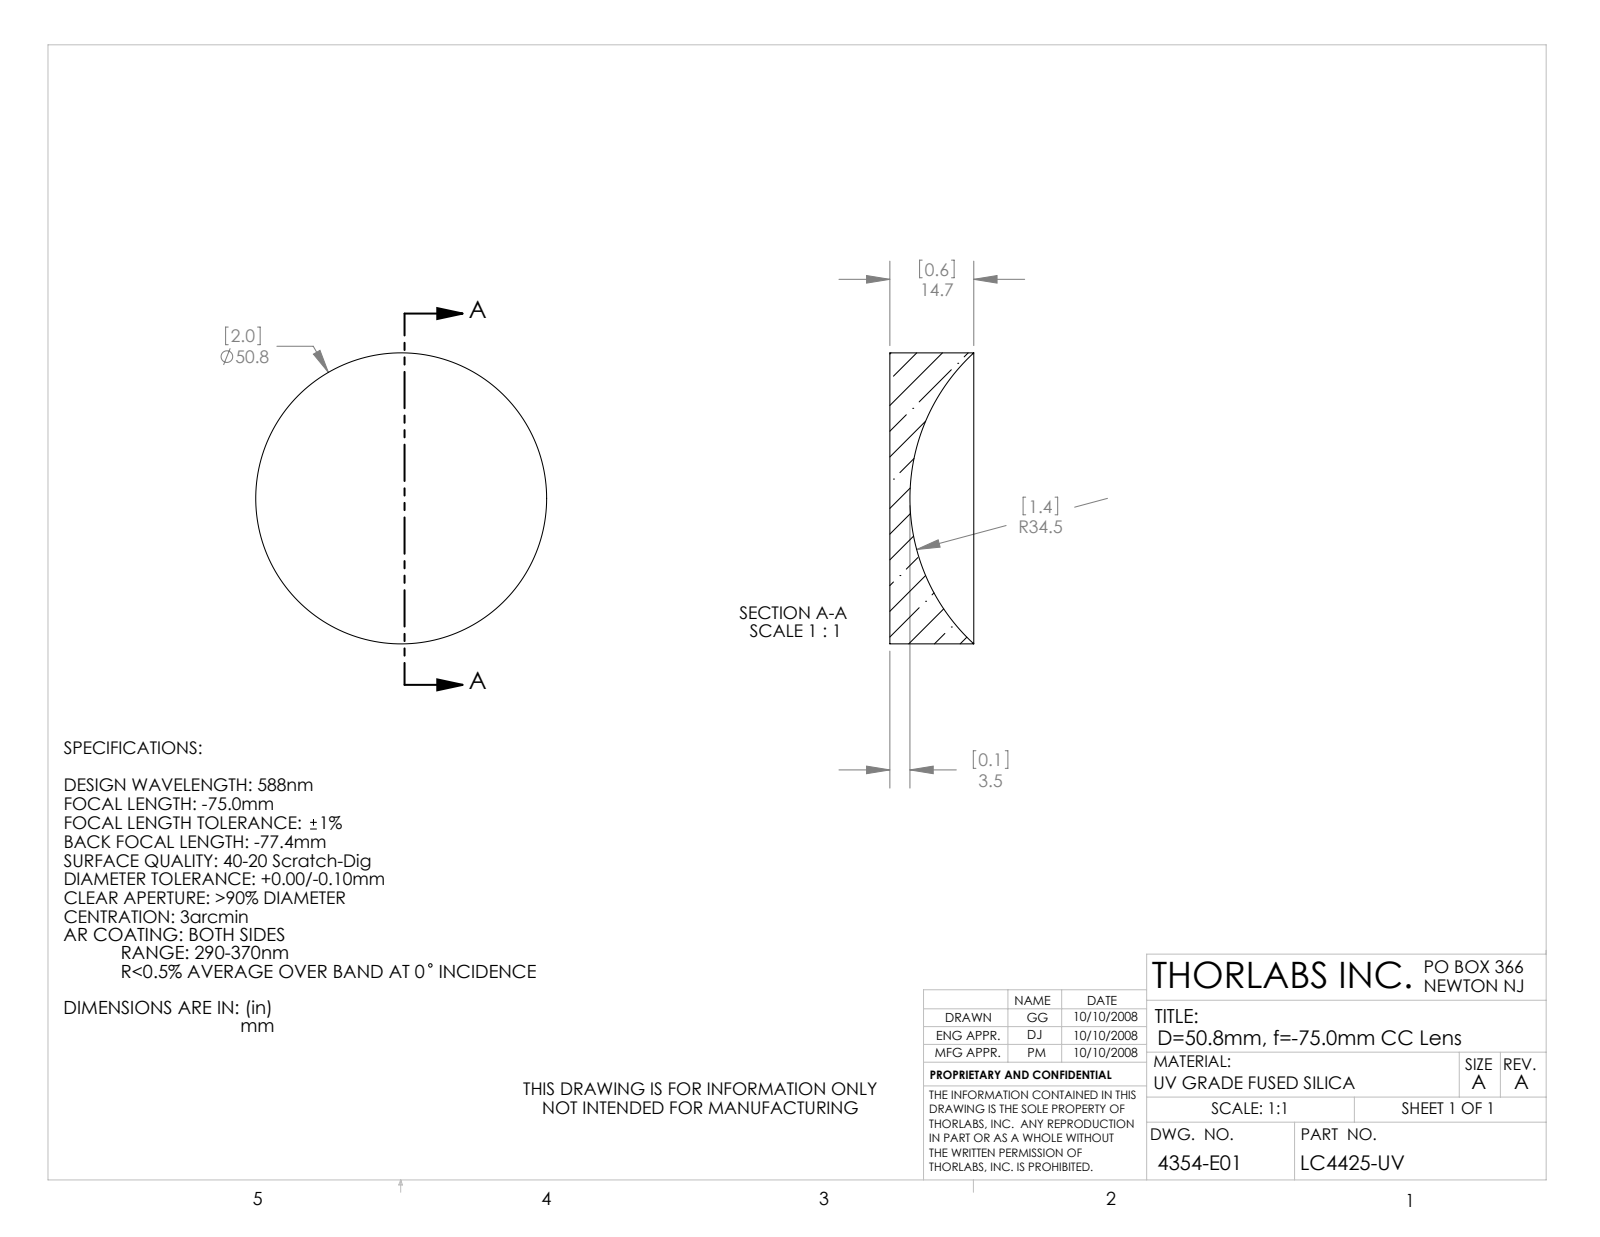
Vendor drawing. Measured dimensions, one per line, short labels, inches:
name: 4354-E0W
written by: SolidWorks 2007 (CONFIG_CONTROL_DESIGN)
unit: in
bodies: 1 solid, 5 faces (1 planar, 2 cylindrical, 2 other)
size: 2 × 2 × 0.577
volume: 1.078 in³; area: 10.51 in²
bosses: 1× ⌀2
